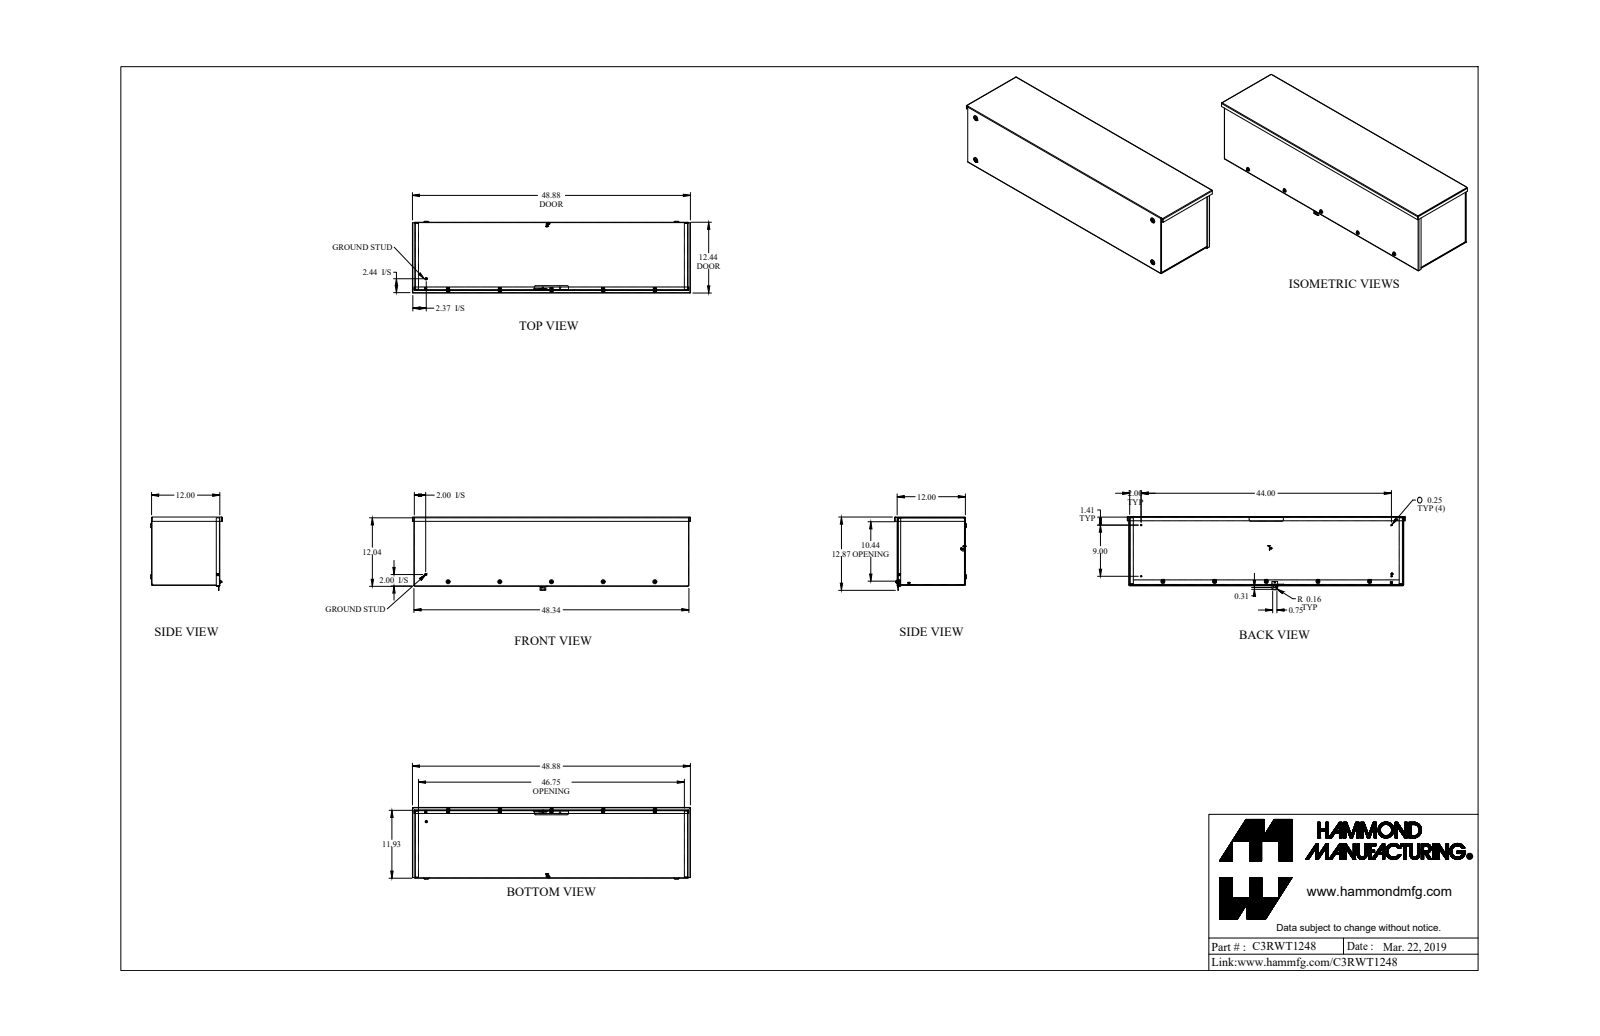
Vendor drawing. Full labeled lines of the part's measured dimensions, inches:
Part name (STEP PRODUCT): C3RWT1248_Default
STEP written by: SolidWorks 2019 (CONFIG_CONTROL_DESIGN)
Units: inches
Bodies: 28 solids, 1006 faces (557 planar, 313 cylindrical, 136 other)
Overall size (bounding box): 48.875 × 12.871 × 12.594
Volume: 201.3 in³ · Surface area: 5 632 in²
Round holes (diameter × count): ⌀0.156 ×7, ⌀0.25 ×6, ⌀0.214 ×5, ⌀0.23 ×5, ⌀0.203 ×2, ⌀0.125 ×1, ⌀0.137 ×1, ⌀0.2 ×1, ⌀0.215 ×1
Round bosses / shafts (diameter × count): ⌀0.19 ×6, ⌀0.148 ×5, ⌀0.375 ×2, ⌀0.5 ×1, ⌀0.367 ×1, ⌀0.21 ×1, ⌀0.152 ×1, ⌀0.125 ×1
Partial cylindrical surfaces — rounded edges, fillets, slot ends (radius × count): R0.08 ×20, R0.108 ×20, R0.036 ×18, R0.108 ×18, R0.125 ×13, R0.022 ×10, R0.25 ×6, R0.171 ×5
Main face-to-face distances: 0.072, 11.928, 11.856, 12, 47.928, 48, 47.856, 0.172, 0.144, 11.784
Hole centre spacings: 9.086, 9.086, 18.172, 27.258, 3.927, 12.822, 12.944, 16.11
